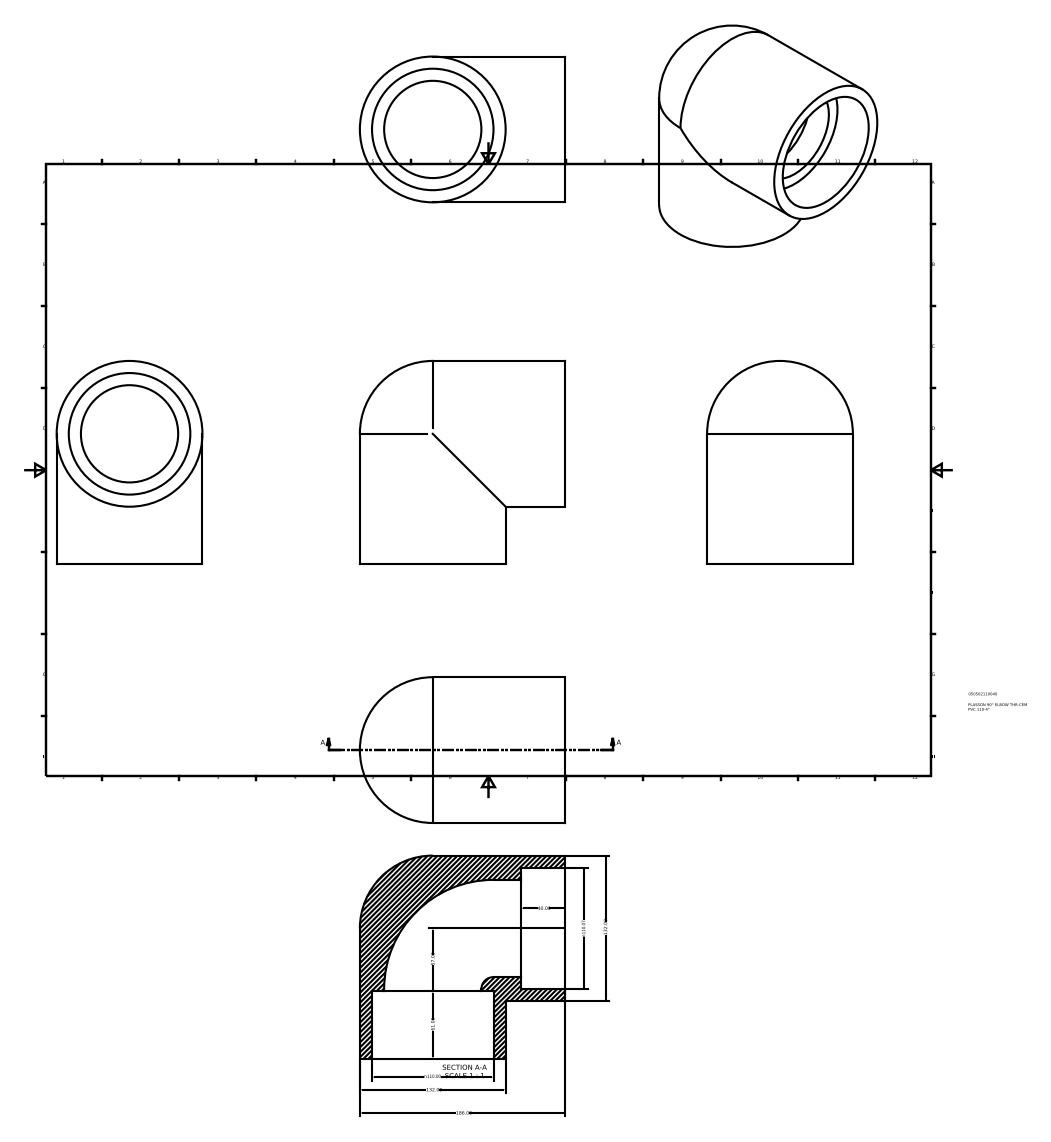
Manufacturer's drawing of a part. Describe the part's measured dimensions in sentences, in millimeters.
The part is named "050502110040". Its 3-D file was written by "Autodesk Inventor 2015 (AUTOMOTIVE_DESIGN)". It is 1 solid with 12 faces: 4 planar, 6 cylindrical and 2 other. Overall it measures 186 by 184 by 132 millimeters. Its volume is 1 524 000 cubic millimeters and its surface area 176 424 square millimeters. Round holes: 2 of diameter 88.06, 1 of diameter 110, 1 of diameter 110.07. Round bosses or shafts: 2 of diameter 132. The main face-to-face distances are 40, 61.
